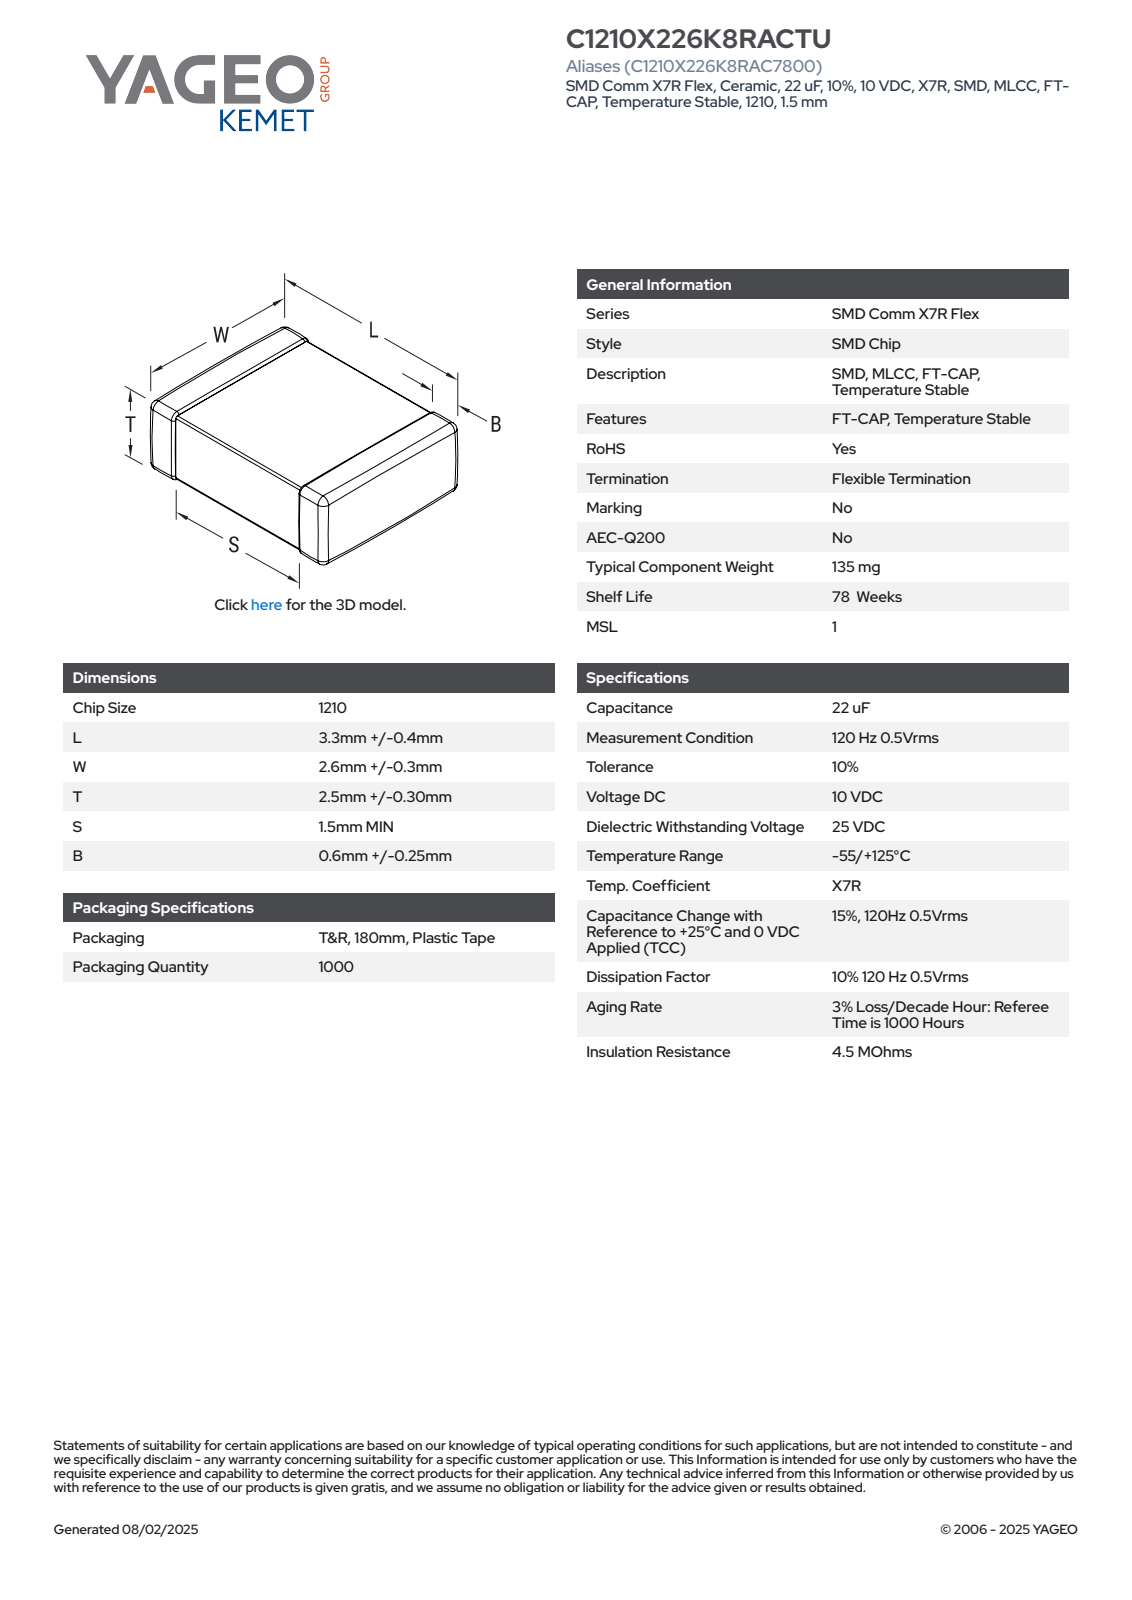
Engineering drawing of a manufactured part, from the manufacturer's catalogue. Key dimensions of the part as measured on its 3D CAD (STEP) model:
Part name (STEP PRODUCT): CCS_CCSTD_1210_L3.7W2.9T2.8B0.6
STEP written by: SolidWorks 2021 (AUTOMOTIVE_DESIGN)
Units: millimetres
Bodies: 4 solids, 129 faces (71 planar, 42 cylindrical, 16 other)
Overall size (bounding box): 3.7 × 2.9 × 2.8
Volume: 29 mm³ · Surface area: 58 mm²
Main face-to-face distances: 2.74, 2.84, 3.7, 2.68, 2.78, 2.8, 2.9, 0.43, 1.57, 2.13
